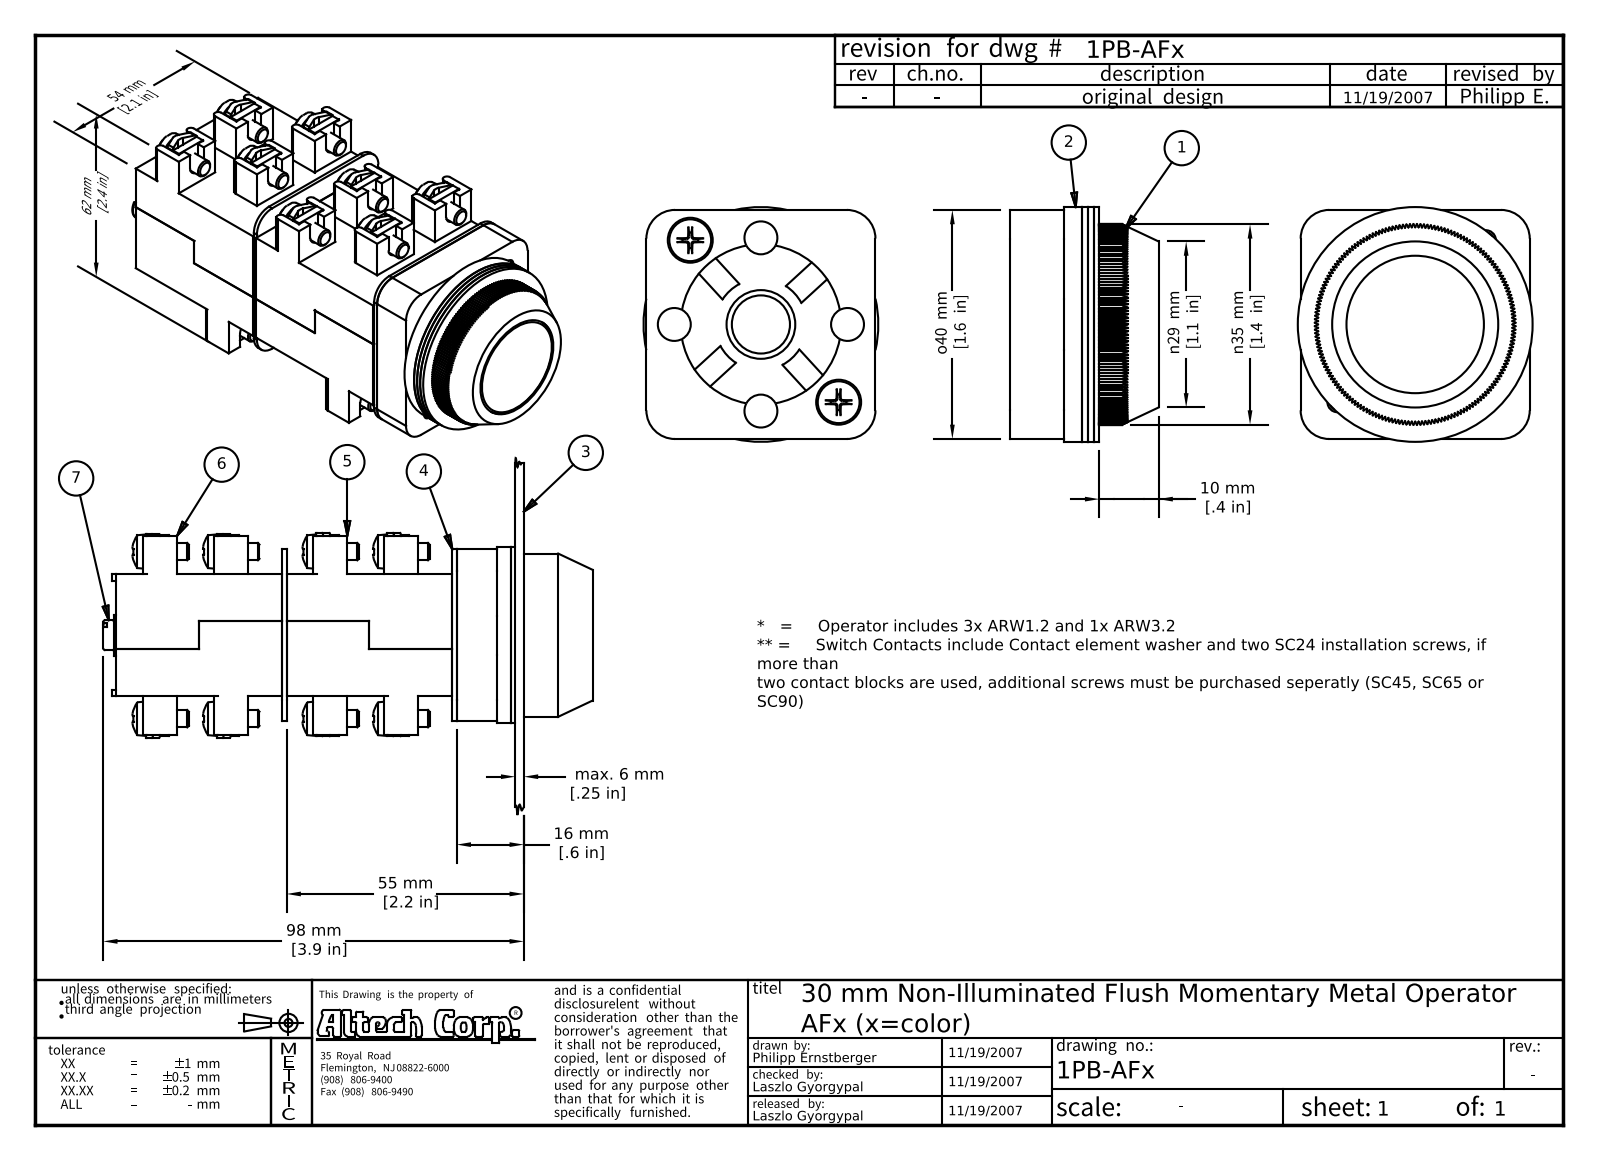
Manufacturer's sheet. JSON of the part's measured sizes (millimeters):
{"part_name": "AFx; base; rubber_gasket_3mm; rubber_gasket_1mm (+2 more)", "step_written_by": "Autodesk Inventor 2008 (AUTOMOTIVE_DESIGN)", "units": "millimeters", "bodies": {"solids": 8, "faces": 705, "planar": 427, "cylindrical": 222, "other": 56}, "overall_size": [41, 41, 26], "volume_mm3": 29570, "surface_area_mm2": 18244, "round_holes": [[5.75, 2], [3.5, 1], [7.85, 1], [12, 1], [24, 1], [24.5, 1], [30, 1], [30.5, 1], [31, 1]], "round_bosses_or_shafts": [[7.3, 2], [3.13, 2], [41, 1], [10.15, 1], [3.5, 1]], "partial_cylinders_radius": [[5, 4], [13.75, 1], [14, 1], [17.5, 1]], "face_to_face_distances": [1, 2, 12.65, 3.15, 5.15, 4.15, 13.65, 9.5, 3, 6.15], "hole_center_spacings": [15.13, 14.96, 19.19, 21.4, 32.28]}
